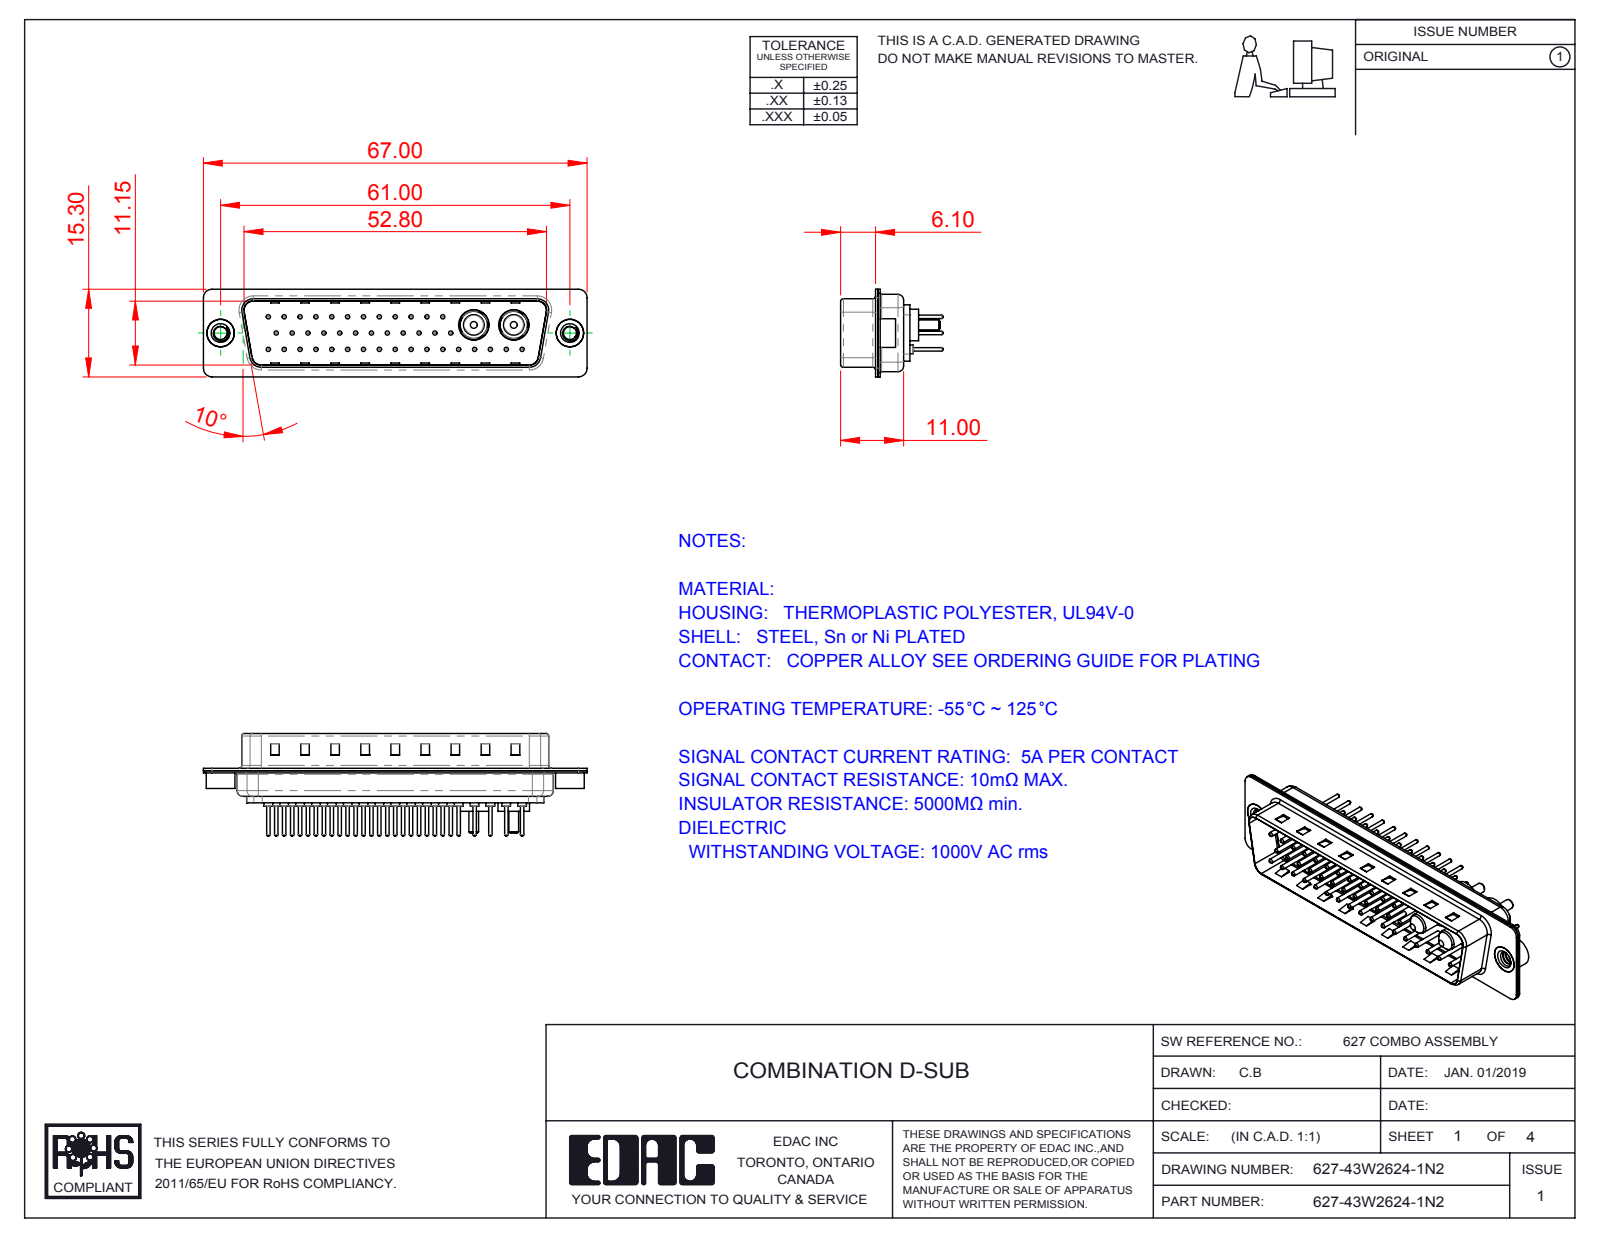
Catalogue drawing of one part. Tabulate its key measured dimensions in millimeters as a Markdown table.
| quantity | value |
| --- | --- |
| part name | 627Combo Threaded Rivet_2; 627Combo Contact Row 1_24; 627Combo Shell Rear_50 Contacts; 627Combo Contact Row 2_24 (+5 more) |
| STEP written by | SolidWorks 2016 (CONFIG_CONTROL_DESIGN) |
| units | millimeters |
| bodies | 50 solids, 2009 faces (510 planar, 753 cylindrical, 746 other) |
| overall size | 67 × 17.9 × 15.3 |
| volume | 4 635 mm³ |
| surface area | 10 711 mm² |
| round holes (diameter × count) | 0.75 × 41, 1.6 × 41, 2 × 41, 2.26 × 2, 4 × 2, 4.8 × 2, 4.85 × 2, 5.3 × 2 |
| round bosses / shafts (diameter × count) | 1.5 × 41, 0.6 × 41, 5.5 × 2, 5.2 × 2, 5 × 2, 4.9 × 2, 4.75 × 2, 3.75 × 2 |
| partial cylindrical surfaces (radius × count) | 1.5 × 16, 2 × 12, 0.5 × 8, 1.6 × 8, 0.25 × 4, 0.6 × 4, 0.65 × 4, 0.9 × 4 |
| main face-to-face distances | 0.4, 11.55, 5.6, 6, 0.78, 4.1, 1.5, 0.77, 12.33, 12.32 |
| hole center spacings | 2.77, 3.16, 5.54, 8.31, 11.08, 13.85, 16.62, 19.39 |
